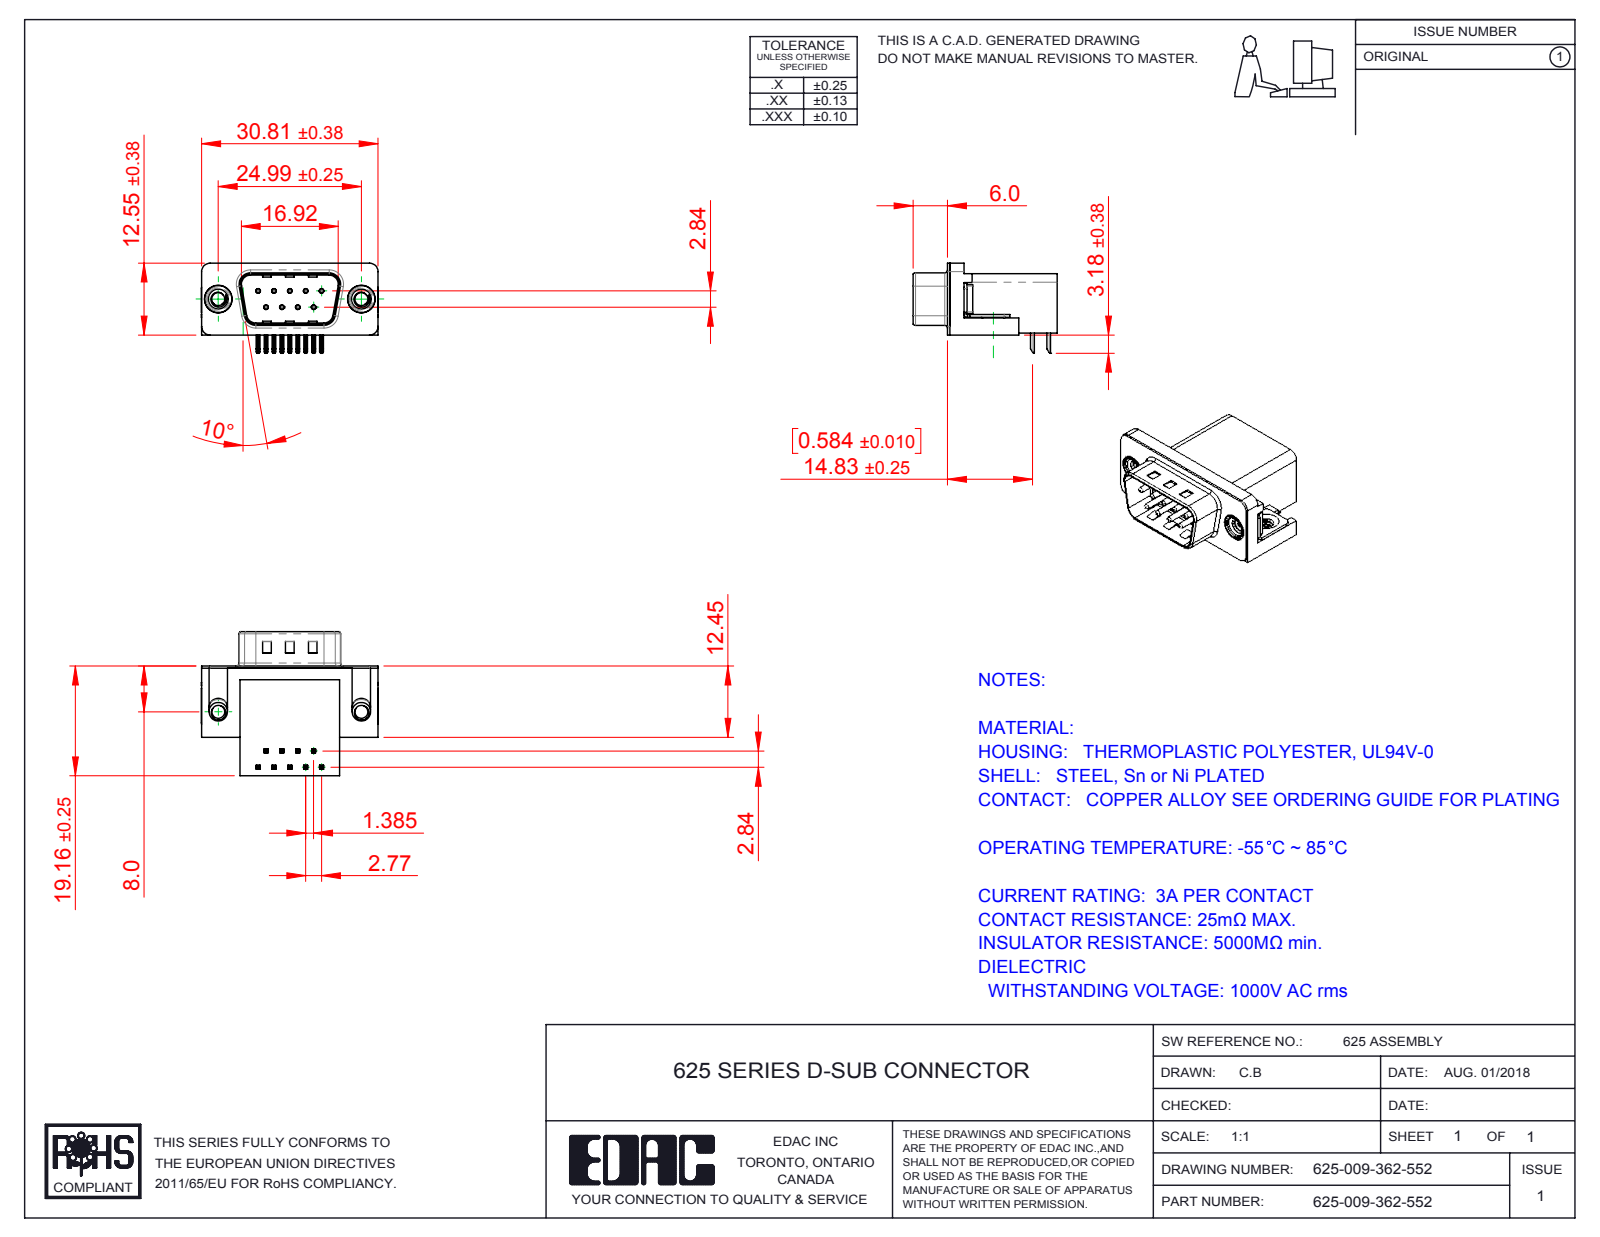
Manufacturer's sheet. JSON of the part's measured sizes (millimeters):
{"part_name": "625-009-362-552; 625 Contact Bottom; 625 Shell_9 Socket; 625 4-40 Threaded Rivet (+3 more)", "step_written_by": "SolidWorks 2016 (CONFIG_CONTROL_DESIGN)", "units": "millimeters", "bodies": {"solids": 15, "faces": 1025, "planar": 575, "cylindrical": 329, "other": 121}, "overall_size": [30.89, 25.16, 15.73], "volume_mm3": 4488, "surface_area_mm2": 5031, "round_holes": [[0.35, 9], [0.8, 9], [2.26, 4], [4, 2], [4.8, 2], [5, 2]], "round_bosses_or_shafts": [[0.75, 9], [4.9, 2], [4.75, 2], [3.9, 2], [3.26, 2]], "partial_cylinders_radius": [[0.25, 44], [0.12, 18], [1, 16], [0.5, 9], [1.5, 8], [1.6, 8], [0.9, 4], [2, 4]], "face_to_face_distances": [0.4, 10.34, 18.76, 19.16, 2.9, 16.26, 2.5, 0.35, 10.69, 6.7], "hole_center_spacings": [3.16, 2.77, 5.54, 5.03, 5.04, 8.31, 7.48, 7.49]}
